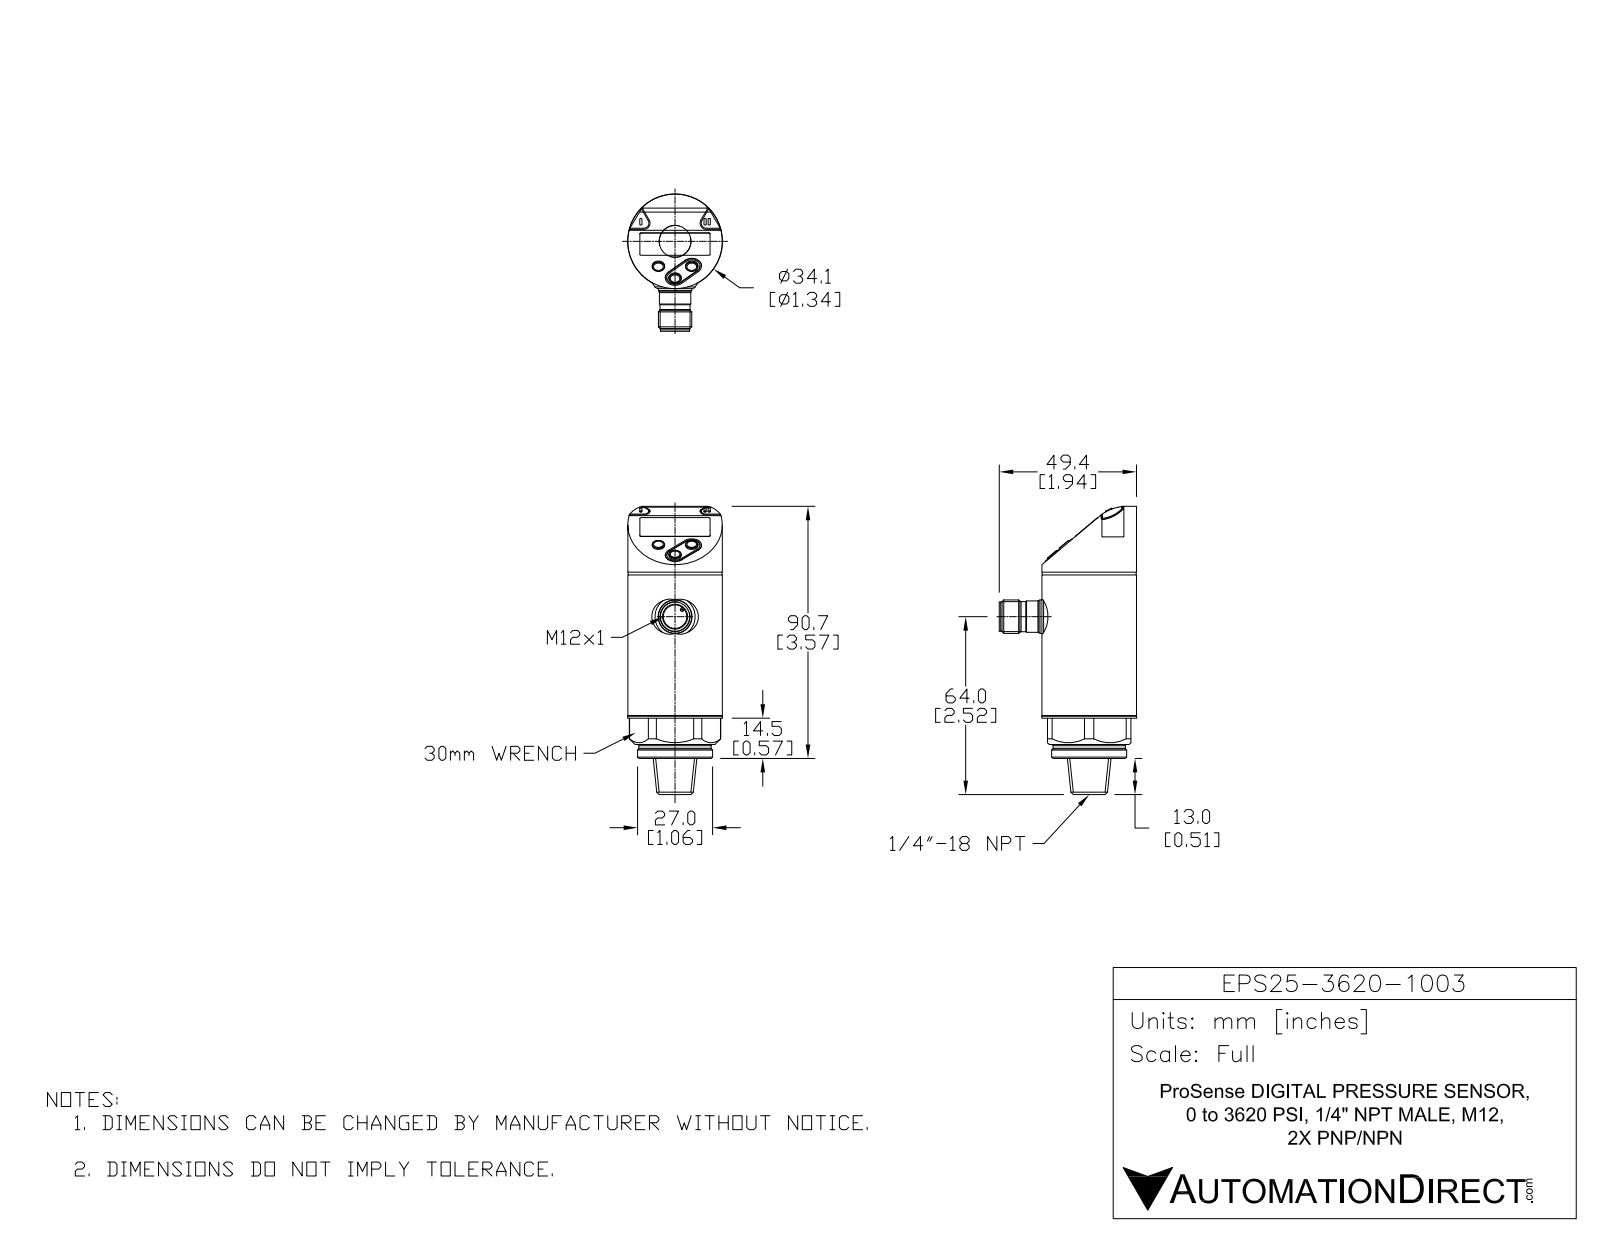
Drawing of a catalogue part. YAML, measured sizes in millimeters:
part_name: "EPS25-3620-1003"
step_written_by: "SolidWorks 2016 (AUTOMOTIVE_DESIGN)"
units: millimeters
bodies: {solids: 11, faces: 370, planar: 207, cylindrical: 84, other: 79}
overall_size: [103.7, 49.4, 34.1]
volume: 72203
surface_area: 21365
round_holes:
  - {diameter: 4.2, count: 1}
  - {diameter: 8.45, count: 1}
round_bosses_or_shafts:
  - {diameter: 1.4, count: 4}
  - {diameter: 1, count: 4}
  - {diameter: 34.1, count: 1}
  - {diameter: 34, count: 1}
  - {diameter: 33.8, count: 1}
  - {diameter: 27, count: 1}
  - {diameter: 26, count: 1}
  - {diameter: 12, count: 1}
partial_cylinders:
  - {radius: 1.8, count: 2}
  - {radius: 2.2, count: 2}
  - {radius: 3, count: 2}
  - {radius: 3.5, count: 2}
  - {radius: 15, count: 2}
  - {radius: 0.61, count: 1}
  - {radius: 6.8, count: 1}
  - {radius: 16.44, count: 1}
face_to_face_distances: [0.68, 11.5, 12.18, 10.68, 1.5, 10, 2, 2.5, 14, 4]
